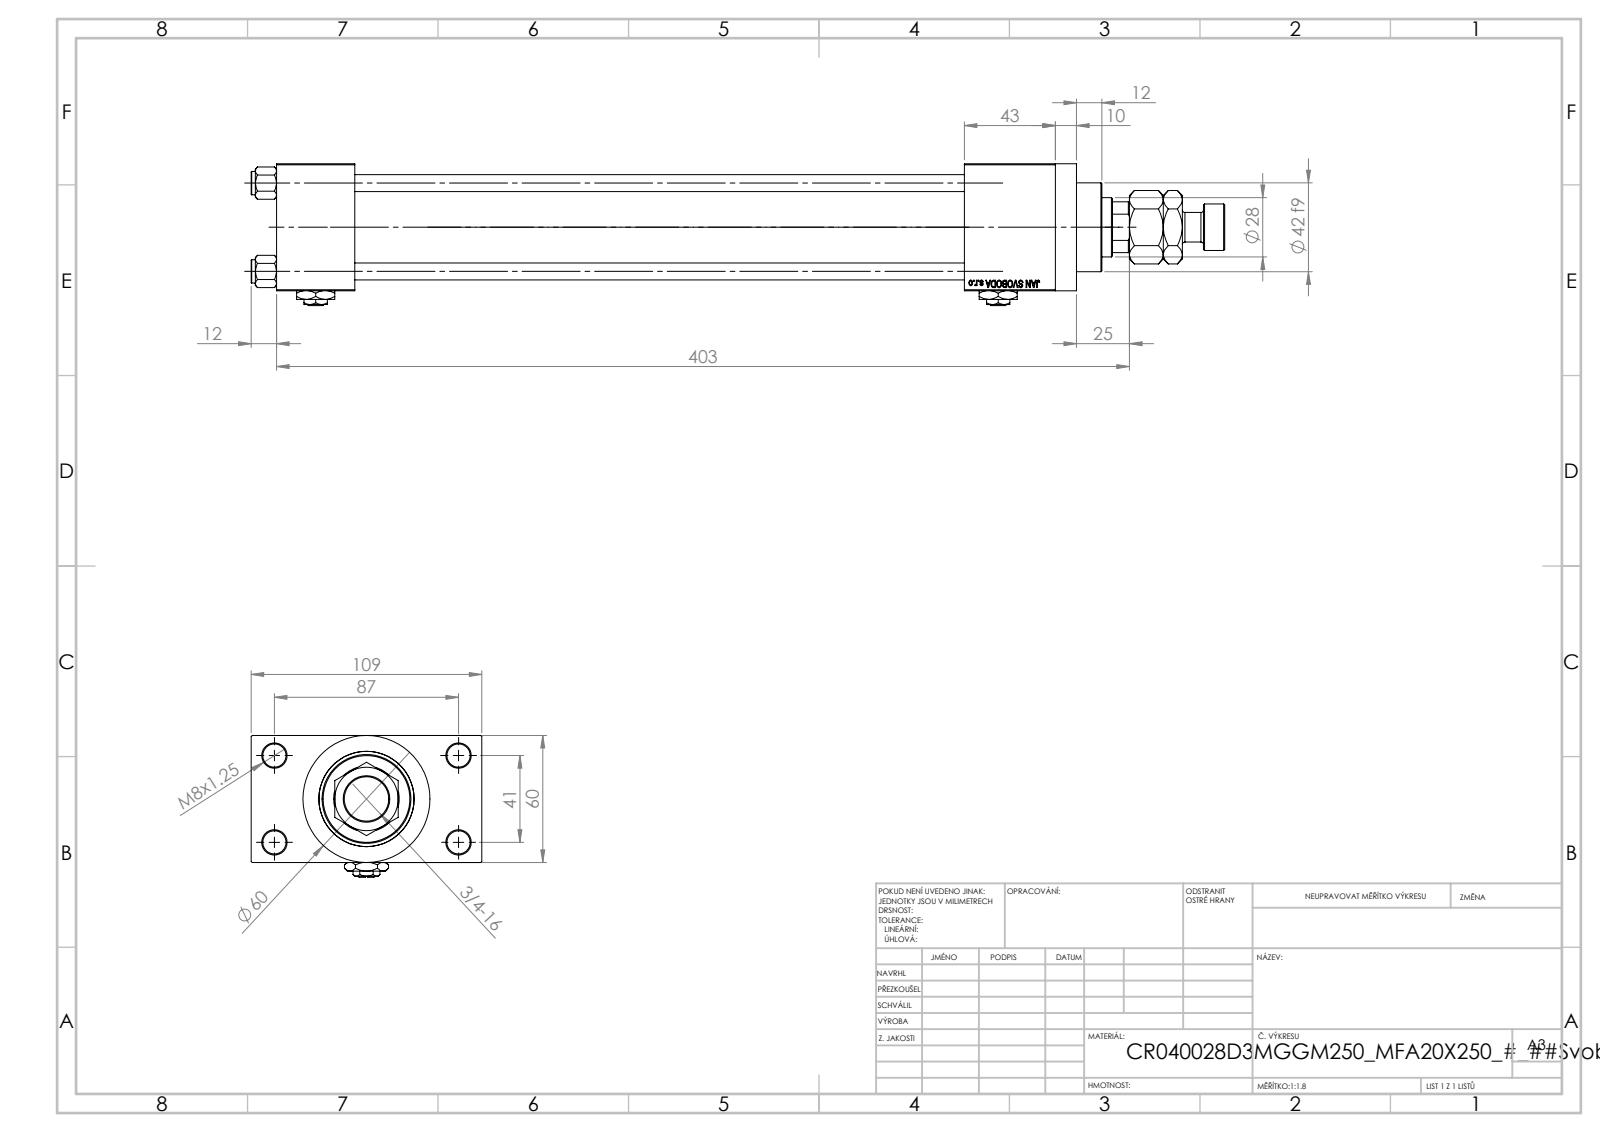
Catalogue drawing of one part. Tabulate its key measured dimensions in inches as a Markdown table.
| quantity | value |
| --- | --- |
| part name | MFA; Zatka_pro_OIL_PORT; V215_VC_A; V215CR_D_TYCINKA (+3 more) |
| STEP written by | SolidWorks 2019 (CONFIG_CONTROL_DESIGN) |
| units | inches |
| bodies | 14 solids, 1258 faces (562 planar, 104 cylindrical, 592 other) |
| overall size | 18.11 × 4.291 × 2.638 |
| volume | 51.12 in³ |
| surface area | 374.4 in² |
| round holes (diameter × count) | 0.315 × 4, 0.433 × 4, 0.276 × 2, 0.656 × 2, 0.945 × 2, 0.728 × 1, 1.102 × 1, 1.22 × 1, 1.575 × 1, 1.772 × 1 |
| round bosses / shafts (diameter × count) | 0.433 × 4, 2.362 × 1, 1.811 × 1, 1.654 × 1, 0.866 × 1, 0.551 × 1 |
| partial cylindrical surfaces (radius × count) | 0.531 × 1 |
| main face-to-face distances | 2.362, 0.965, 3.327, 11.339, 1.457, 12.795, 1.693, 14.488, 13.031, 4.291 |
| hole center spacings | 0.892, 1.161, 1.642, 1.856, 1.893, 2.533, 3.011, 1.614 |
